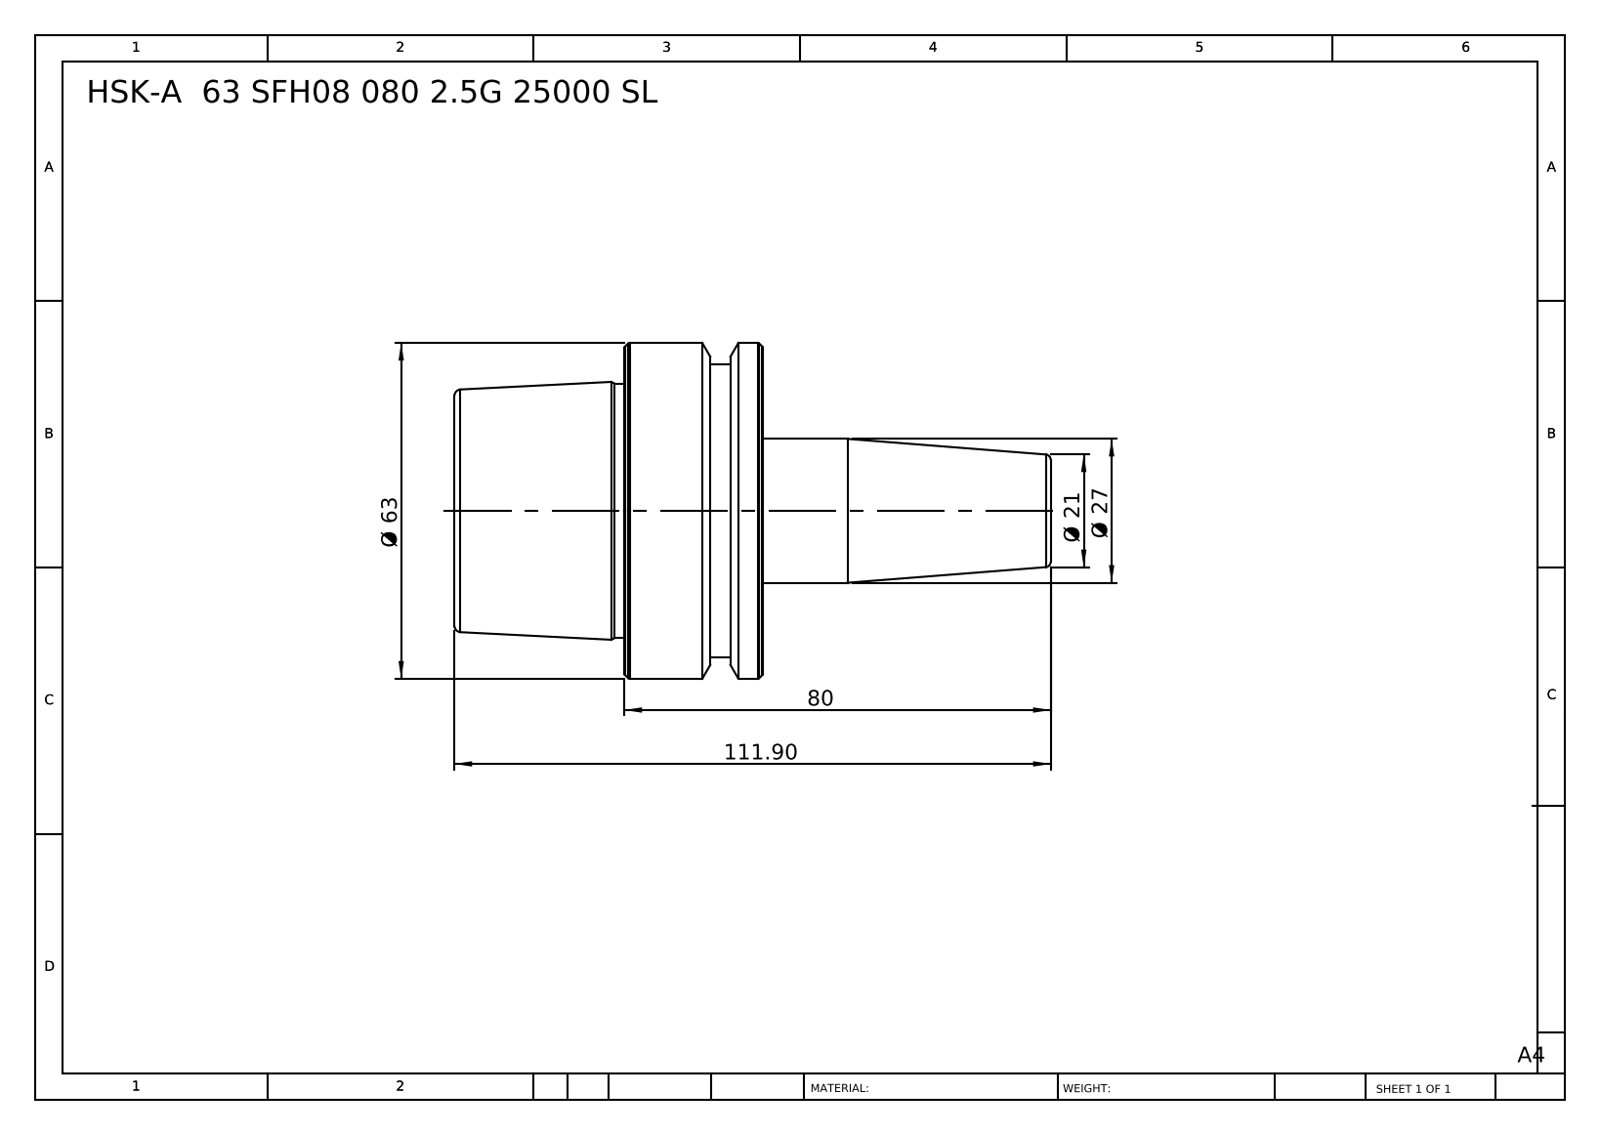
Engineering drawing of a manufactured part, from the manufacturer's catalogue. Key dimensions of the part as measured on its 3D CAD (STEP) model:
Part name (STEP PRODUCT): HSK-A 63 SFH08 080 2.5G 25000 SL
STEP written by: SolidWorks 2014 (CONFIG_CONTROL_DESIGN)
Units: millimetres
Bodies: 1 solid, 46 faces (6 planar, 10 cylindrical, 30 other)
Overall size (bounding box): 111.9 × 63 × 63
Volume: 159 012 mm³ · Surface area: 20 629 mm²
Round bosses / shafts (diameter × count): ⌀63 ×1, ⌀55 ×1, ⌀47.78 ×1, ⌀27 ×1
Main face-to-face distances: 57.9, 26, 31.9, 54, 80, 111.9, 60.1, 6.1, 19.9, 51.8
